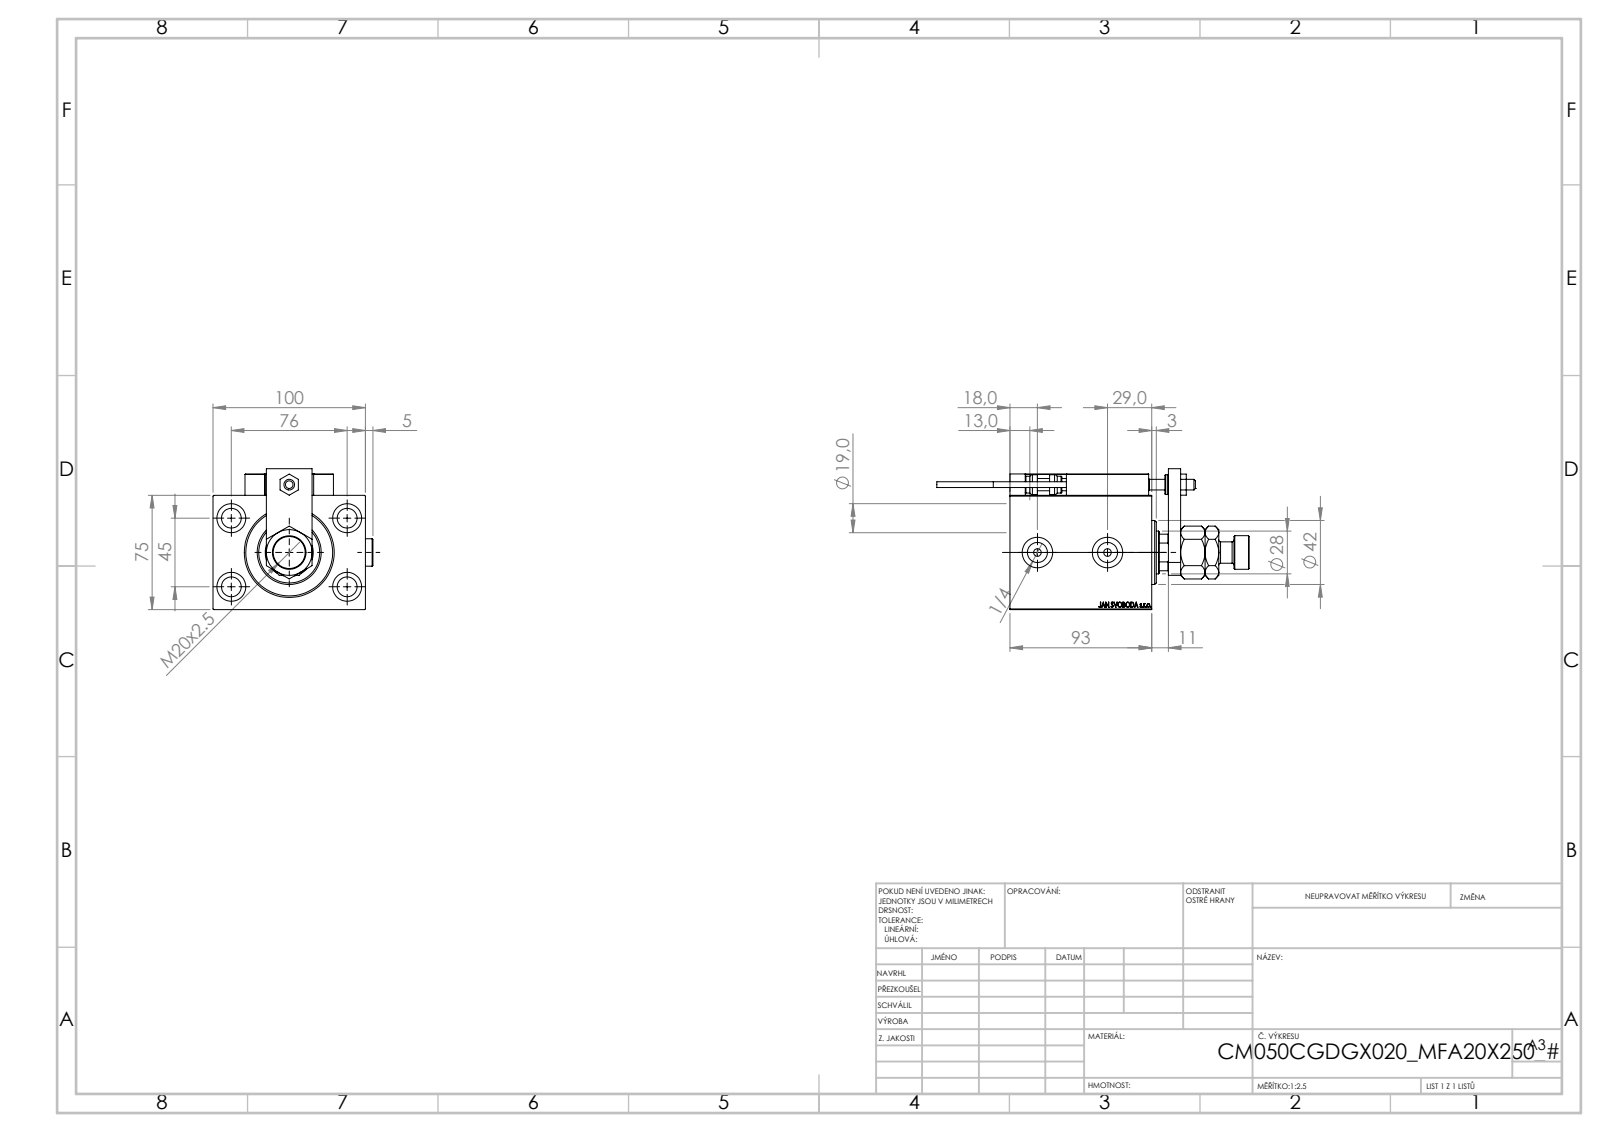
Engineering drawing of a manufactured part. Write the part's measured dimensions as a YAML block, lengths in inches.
part_name: "MAGNET; Zatka_OIL_PORT; Block; TYC_L79 (+7 more)"
step_written_by: "SolidWorks 2019 (CONFIG_CONTROL_DESIGN)"
units: inches
bodies: {solids: 26, faces: 1389, planar: 611, cylindrical: 208, other: 570}
overall_size: [8.071, 4.13, 3.642]
volume: 42.28
surface_area: 203.6
round_holes:
  - {diameter: 0.315, count: 5}
  - {diameter: 0.126, count: 4}
  - {diameter: 0.157, count: 4}
  - {diameter: 0.197, count: 4}
  - {diameter: 0.512, count: 4}
  - {diameter: 0.748, count: 4}
  - {diameter: 0.787, count: 3}
  - {diameter: 0.518, count: 2}
  - {diameter: 0.276, count: 1}
  - {diameter: 0.728, count: 1}
  - {diameter: 1.102, count: 1}
  - {diameter: 1.24, count: 1}
round_bosses_or_shafts:
  - {diameter: 0.709, count: 2}
  - {diameter: 0.197, count: 2}
  - {diameter: 0.15, count: 2}
  - {diameter: 1.654, count: 1}
  - {diameter: 0.866, count: 1}
  - {diameter: 0.551, count: 1}
  - {diameter: 0.512, count: 1}
  - {diameter: 0.433, count: 1}
partial_cylinders:
  - {radius: 0.012, count: 30}
  - {radius: 0.118, count: 2}
  - {radius: 0.531, count: 1}
face_to_face_distances: [2.953, 3.937, 3.661, 2.008, 1.654, 0.315, 0.551, 0.512, 2.756, 0.394]
hole_center_spacings: [1.739, 0.448, 0.787, 1.165, 1.169, 1.42, 1.661, 1.729]
